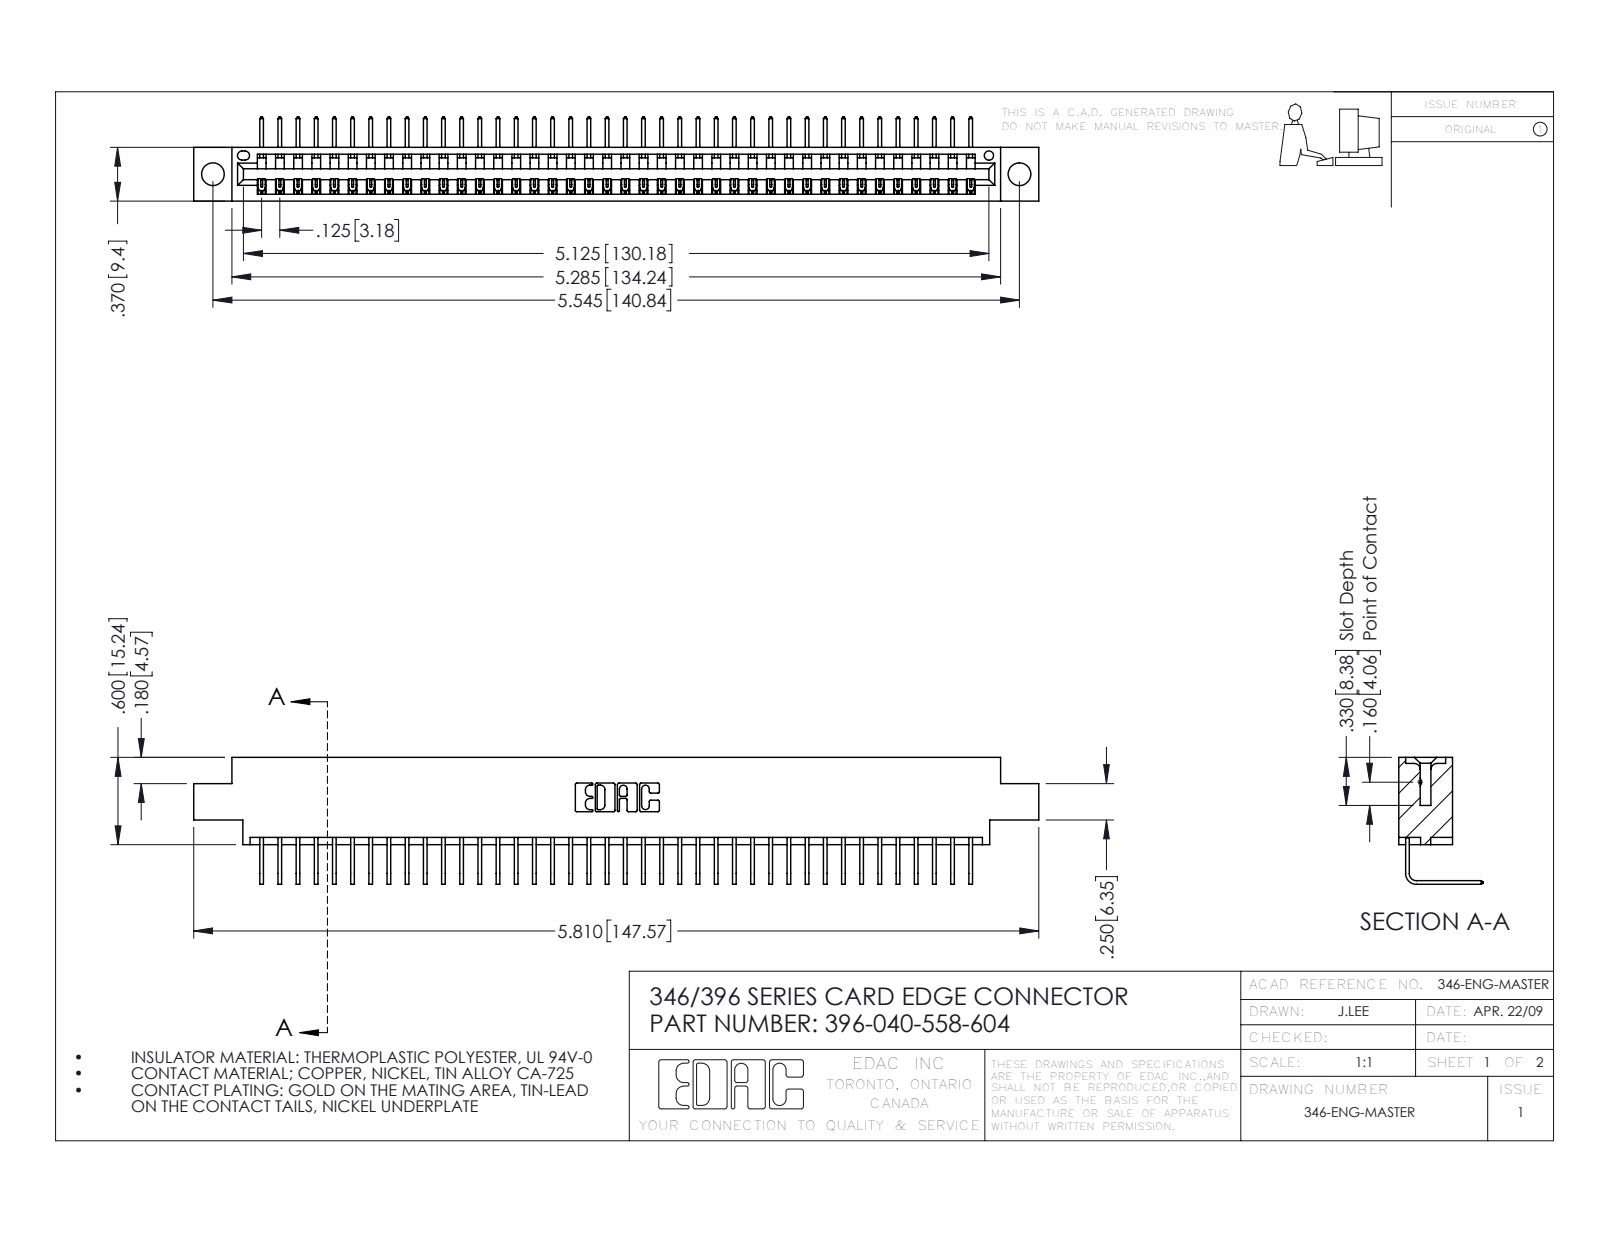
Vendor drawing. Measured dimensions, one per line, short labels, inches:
name: 396-040-558-604; 345-292-001_558 Tail - 2; 346 Part_0.170 Offset - 0.156 Dia-TH
written by: SolidWorks 2016 (CONFIG_CONTROL_DESIGN)
unit: in
bodies: 41 solids, 2526 faces (1760 planar, 766 cylindrical, 0 other)
size: 5.81 × 0.873 × 0.58
volume: 0.855 in³; area: 28.27 in²
holes: 2× ⌀0.156, 1× ⌀0.064
rounds: 80× R0.006, 22× R0.01, 6× R0.007, 6× R0.031, 3× R0.026, 2× R0.031, 2× R0.04, 1× R0.014
face distances: 0.322, 0.048, 0.37, 0.25, 0.298, 0.025, 0.072, 0.148, 0.222, 0.1
hole spacings: 0.246, 5.336, 5.545
